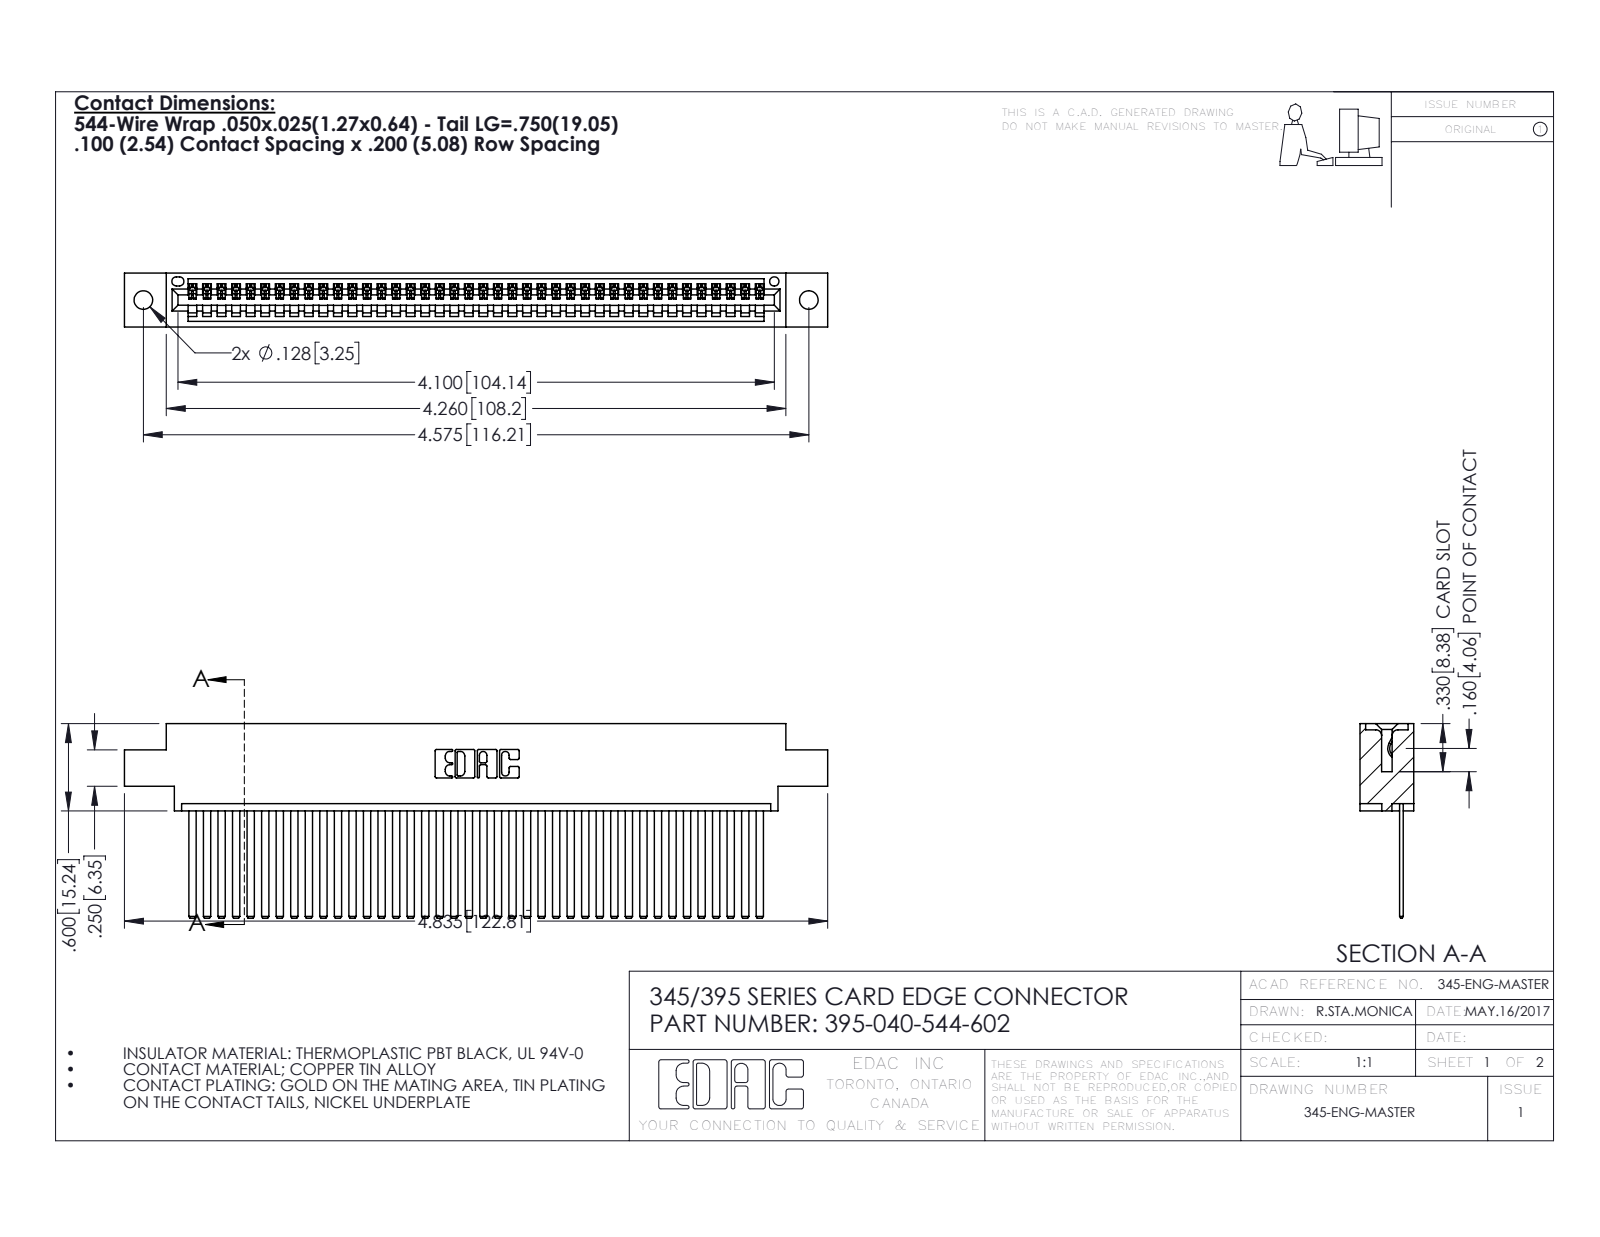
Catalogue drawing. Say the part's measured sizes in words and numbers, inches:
The part is named "345 Part_0.170 Offset - 0.128 Dia; 345-292-001_345-293-144; 395-040-544-602". Its 3-D file was written by "SolidWorks 2016 (CONFIG_CONTROL_DESIGN)". It is 41 solids with 2210 faces: 1524 planar, 686 cylindrical and 0 other. Overall it measures 4.835 by 1.337 by 0.37 inches. Its volume is 0.73 cubic inches and its surface area 26.53 square inches. Round holes: 2 of diameter 0.128, 1 of diameter 0.064. Partial cylindrical surfaces (rounded edges, fillets, slot ends): 80 of radius 0.006, 22 of radius 0.01, 6 of radius 0.007, 6 of radius 0.031, 3 of radius 0.026, 2 of radius 0.031, 2 of radius 0.04, 1 of radius 0.014. The main face-to-face distances are 0.072, 0.298, 0.025, 0.098, 0.272, 0.37, 0.2, 0.225, 0.175, 0.149. The hole center spacings are 0.27, 4.339, 4.575.
